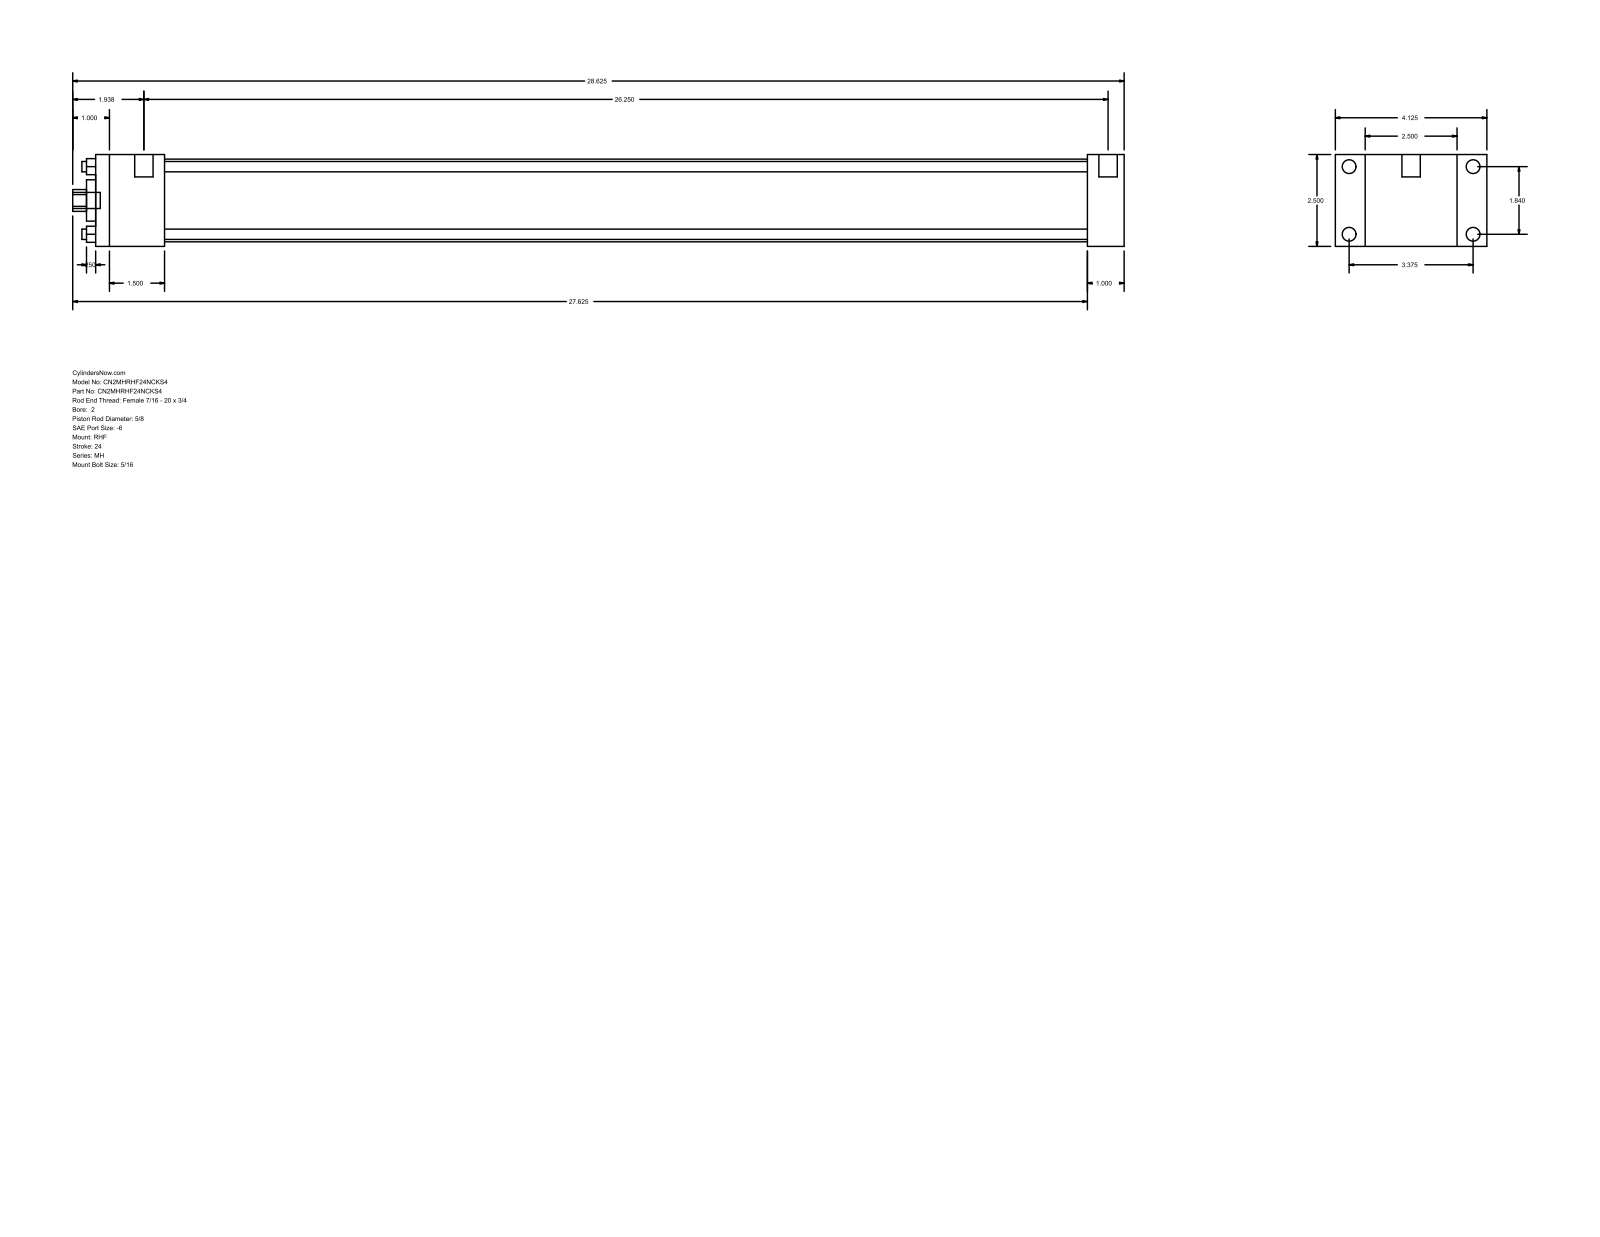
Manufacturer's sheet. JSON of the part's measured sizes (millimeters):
{"part_name": "MH_RHF__0200_0.625", "step_written_by": "GSSL Pune (CONFIG_CONTROL_DESIGN)", "units": "millimeters", "bodies": {"solids": 0, "faces": 88, "planar": 60, "cylindrical": 28, "other": 0}, "overall_size": [727.08, 104.78, 63.5], "round_holes": [[7.14, 4], [15.88, 1], [28.57, 1], [57.15, 1]], "round_bosses_or_shafts": [[9.53, 4], [5.56, 4], [12.7, 2], [11.11, 1]], "partial_cylinders_radius": [[7.54, 1]], "face_to_face_distances": [63.5, 25.41, 20.64, 84.14, 685.79, 711.2, 104.78, 47.62, 638.17, 663.58], "hole_center_spacings": [33.05, 46.74, 66.1]}
